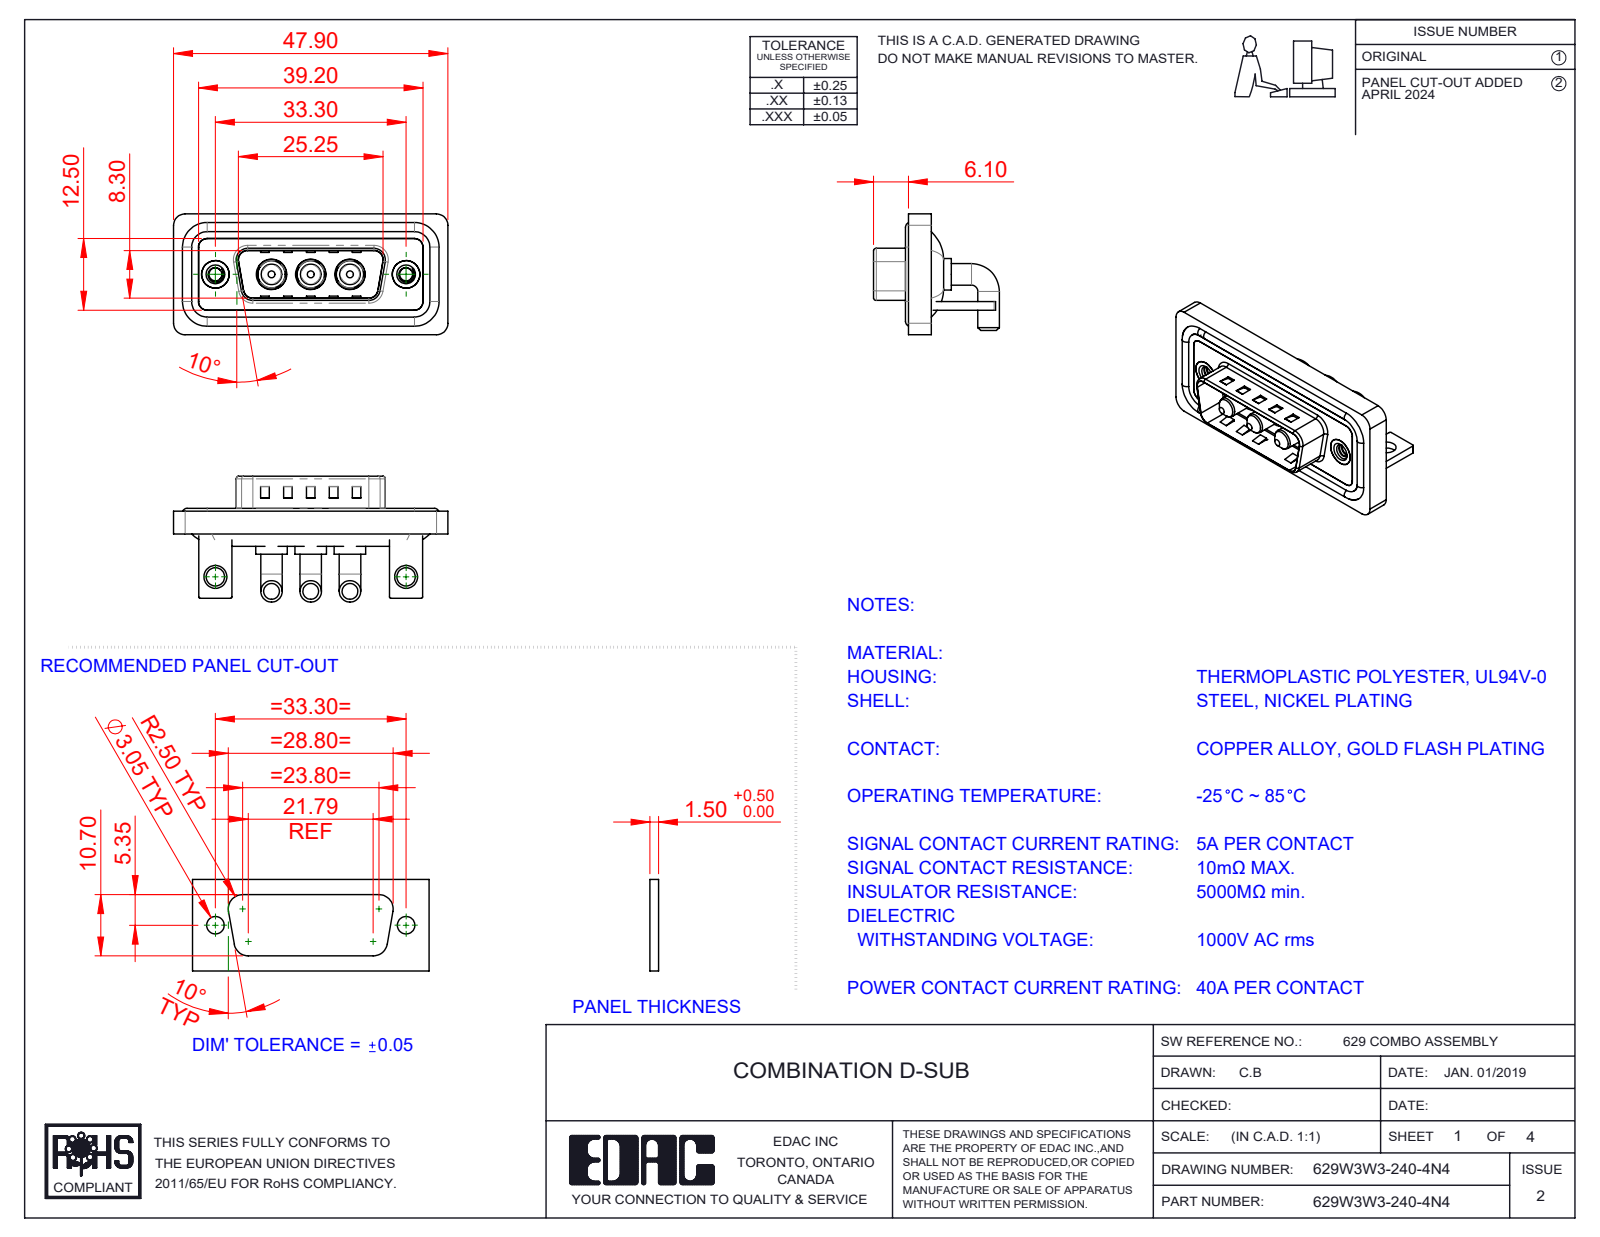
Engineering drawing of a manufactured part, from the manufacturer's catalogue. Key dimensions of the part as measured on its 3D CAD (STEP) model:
Part name (STEP PRODUCT): 629Combo Housing_3W3; Power Pin_40A RA; 629Combo Threaded Rivet_3; 629Combo Waterproof Housing_15 Contacts (+4 more)
STEP written by: SolidWorks 2023 (CONFIG_CONTROL_DESIGN)
Units: millimetres
Bodies: 15 solids, 616 faces (227 planar, 265 cylindrical, 124 other)
Overall size (bounding box): 47.9 × 21.98 × 21.1
Volume: 6 275 mm³ · Surface area: 9 755 mm²
Round holes (diameter × count): ⌀4.85 ×3, ⌀5.3 ×3, ⌀2.26 ×2, ⌀3.2 ×2, ⌀4 ×2, ⌀4.8 ×2, ⌀5 ×2
Round bosses / shafts (diameter × count): ⌀3.75 ×6, ⌀1.6 ×4, ⌀5.5 ×3, ⌀5.2 ×3, ⌀4.75 ×3, ⌀3.6 ×3, ⌀4.9 ×2
Partial cylindrical surfaces — rounded edges, fillets, slot ends (radius × count): R2 ×21, R1.5 ×18, R0.25 ×16, R0.5 ×9, R1.6 ×8, R0.6 ×4, R0.65 ×4, R0.9 ×4
Main face-to-face distances: 0.4, 1.5, 0.8, 2.9, 1.1, 2.1, 3.7, 1.6, 1.2, 4.5
Hole centre spacings: 6.85, 9.8, 16.65, 23.5, 33.3, 13.7
